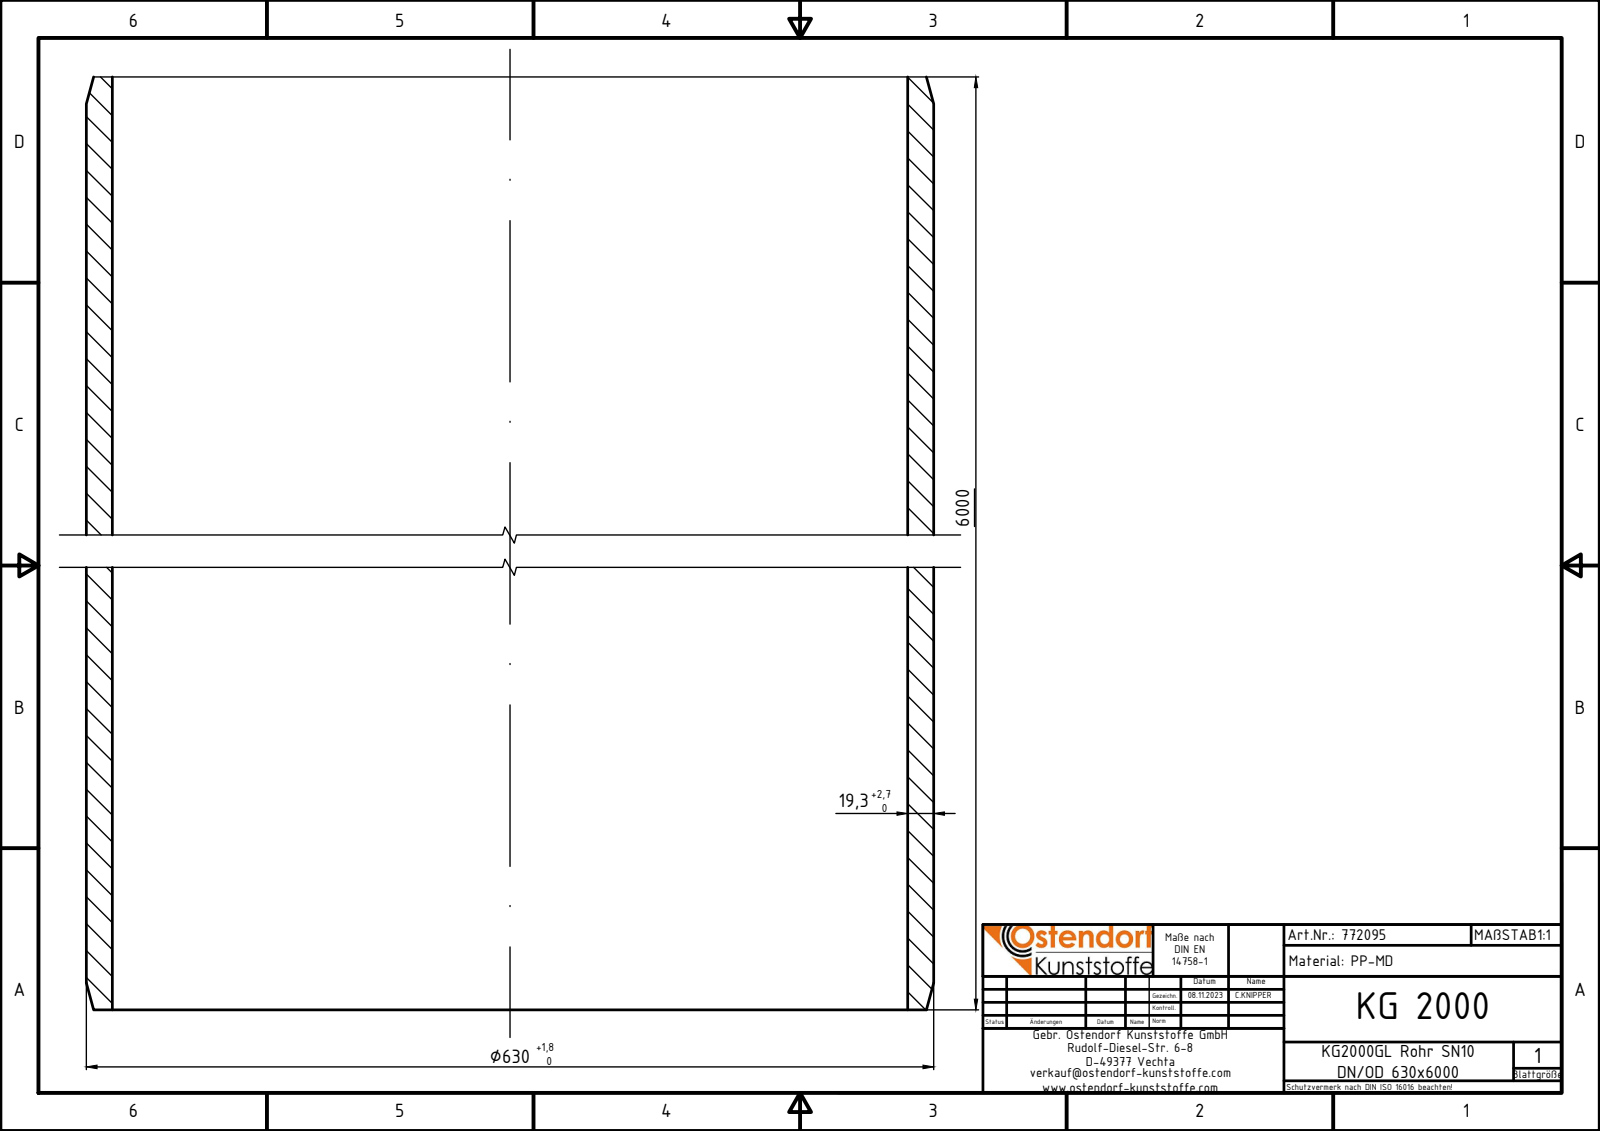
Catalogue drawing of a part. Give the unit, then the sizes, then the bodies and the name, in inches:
Units: inches
Overall size (bounding box): 236.22 × 24.803 × 24.803
Round holes (diameter × count): ⌀23.283 ×1
Round bosses / shafts (diameter × count): ⌀24.803 ×1
Main face-to-face distances: 236.22
Volume: 13 550 in³ · Surface area: 35 770 in²
Bodies: 1 solid, 6 faces (2 planar, 2 cylindrical, 2 other)
Part name (STEP PRODUCT): 772095z
STEP written by: Autodesk Inventor 2024 (AUTOMOTIVE_DESIGN)
